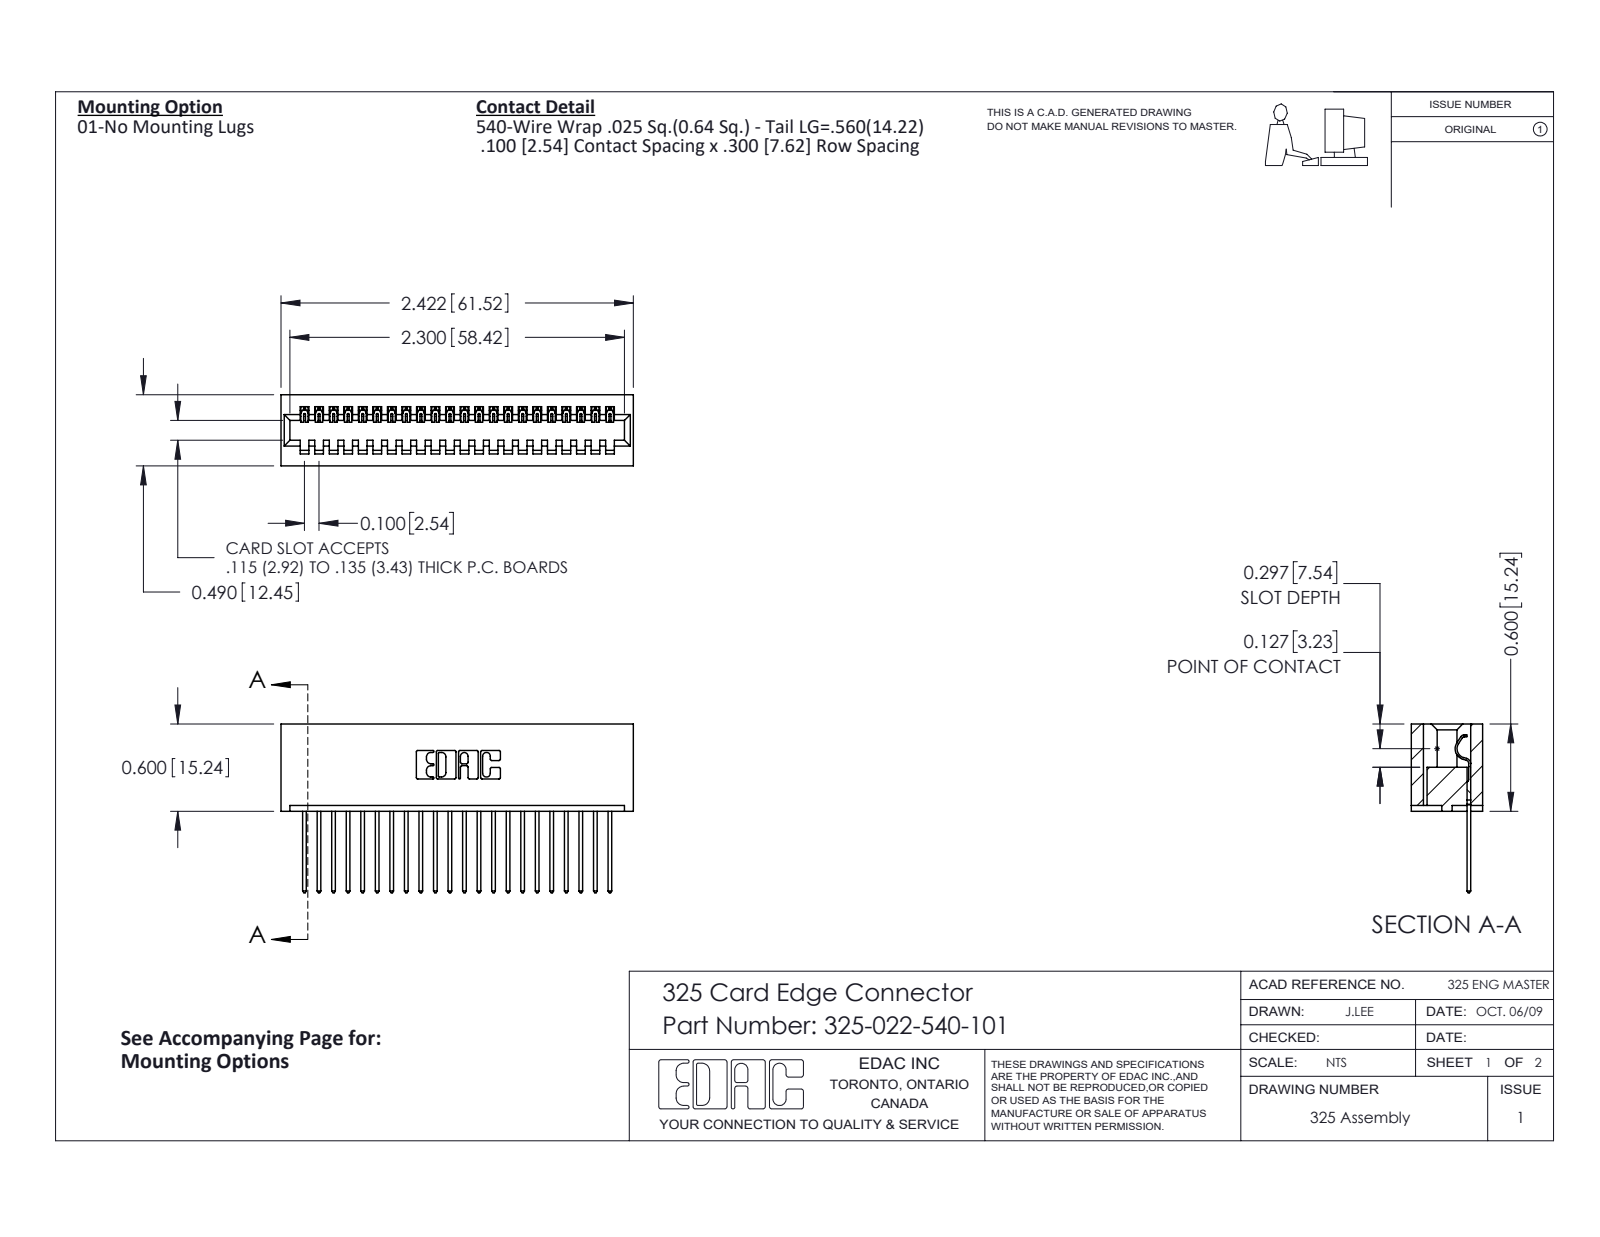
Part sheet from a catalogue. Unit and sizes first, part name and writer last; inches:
Units: inches
Overall size (bounding box): 2.422 × 1.16 × 0.49
Partial cylindrical surfaces — rounded edges, fillets, slot ends (radius × count): R0.006 ×44, R0.01 ×44, R0.01 ×22, R0.007 ×6, R0.031 ×6, R0.026 ×3, R0.014 ×1, R0.022 ×1
Main face-to-face distances: 0.083, 0.407, 0.3, 0.49, 0.107, 0.383, 0.025, 0.1, 0.56, 0.325
Volume: 0.504 in³ · Surface area: 14.55 in²
Bodies: 23 solids, 1382 faces (990 planar, 392 cylindrical, 0 other)
Part name (STEP PRODUCT): 325-022-540-101; 325-292-001_325-293-140; 325 Part_Lugless
STEP written by: SolidWorks 2016 (CONFIG_CONTROL_DESIGN)
